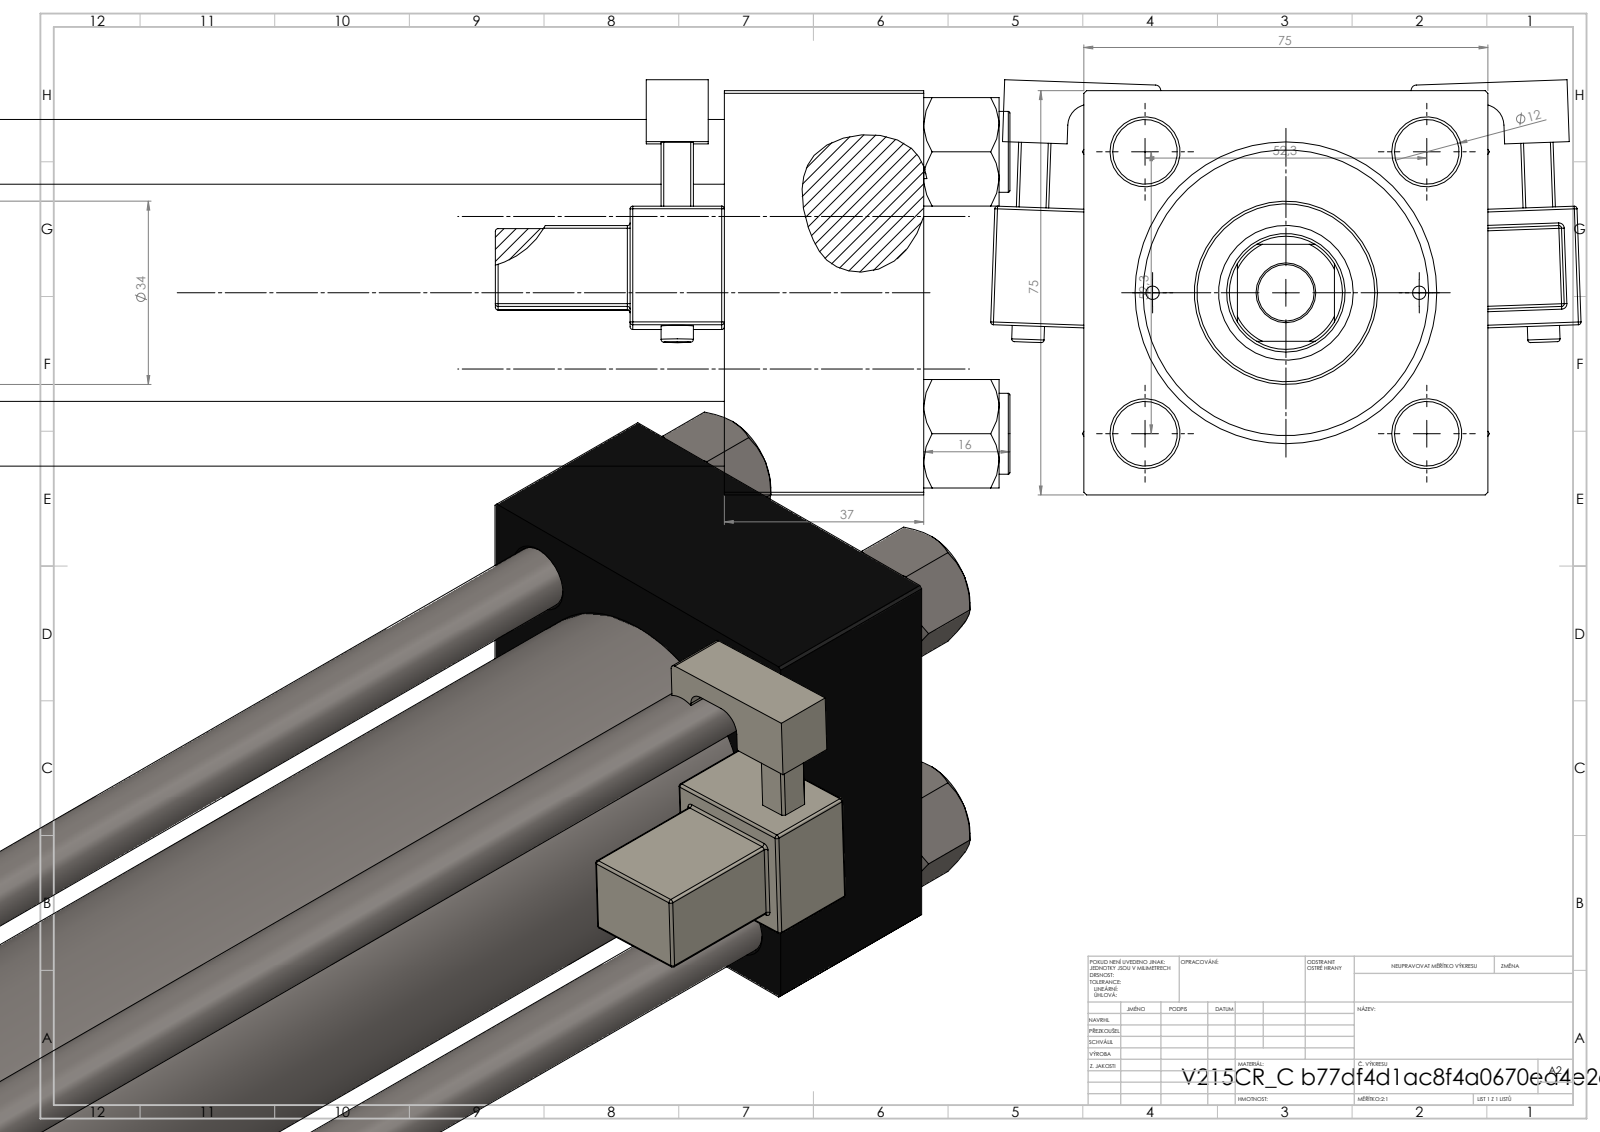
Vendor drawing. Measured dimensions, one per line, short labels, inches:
name: V215CR_C_TYCINKA; V215_VC_A; V215CR_C_Body; V215CR_VCP_C (+2 more)
written by: SolidWorks 2019 (CONFIG_CONTROL_DESIGN)
unit: in
bodies: 13 solids, 1308 faces (586 planar, 150 cylindrical, 572 other)
size: 26.575 × 4.314 × 3.033
volume: 81.59 in³; area: 658.8 in²
holes: 4× ⌀0.472, 2× ⌀0.098, 2× ⌀0.276, 2× ⌀0.825, 2× ⌀1.181, 1× ⌀0.413, 1× ⌀0.866, 1× ⌀0.984, 1× ⌀1.614, 1× ⌀1.969, 1× ⌀2.087
bosses: 4× ⌀0.591, 2× ⌀0.236, 1× ⌀2.205, 1× ⌀1.339
rounds: 48× R0.02, 2× R0.039, 2× R0.098, 2× R0.157, 1× R0.413
face distances: 2.953, 1.457, 24.961, 23.504, 22.638, 21.181, 2.323, 23.831, 22.374, 1.193
hole spacings: 1.031, 1.456, 2.059, 2.253, 0.974, 2.912, 1.949, 22.579
